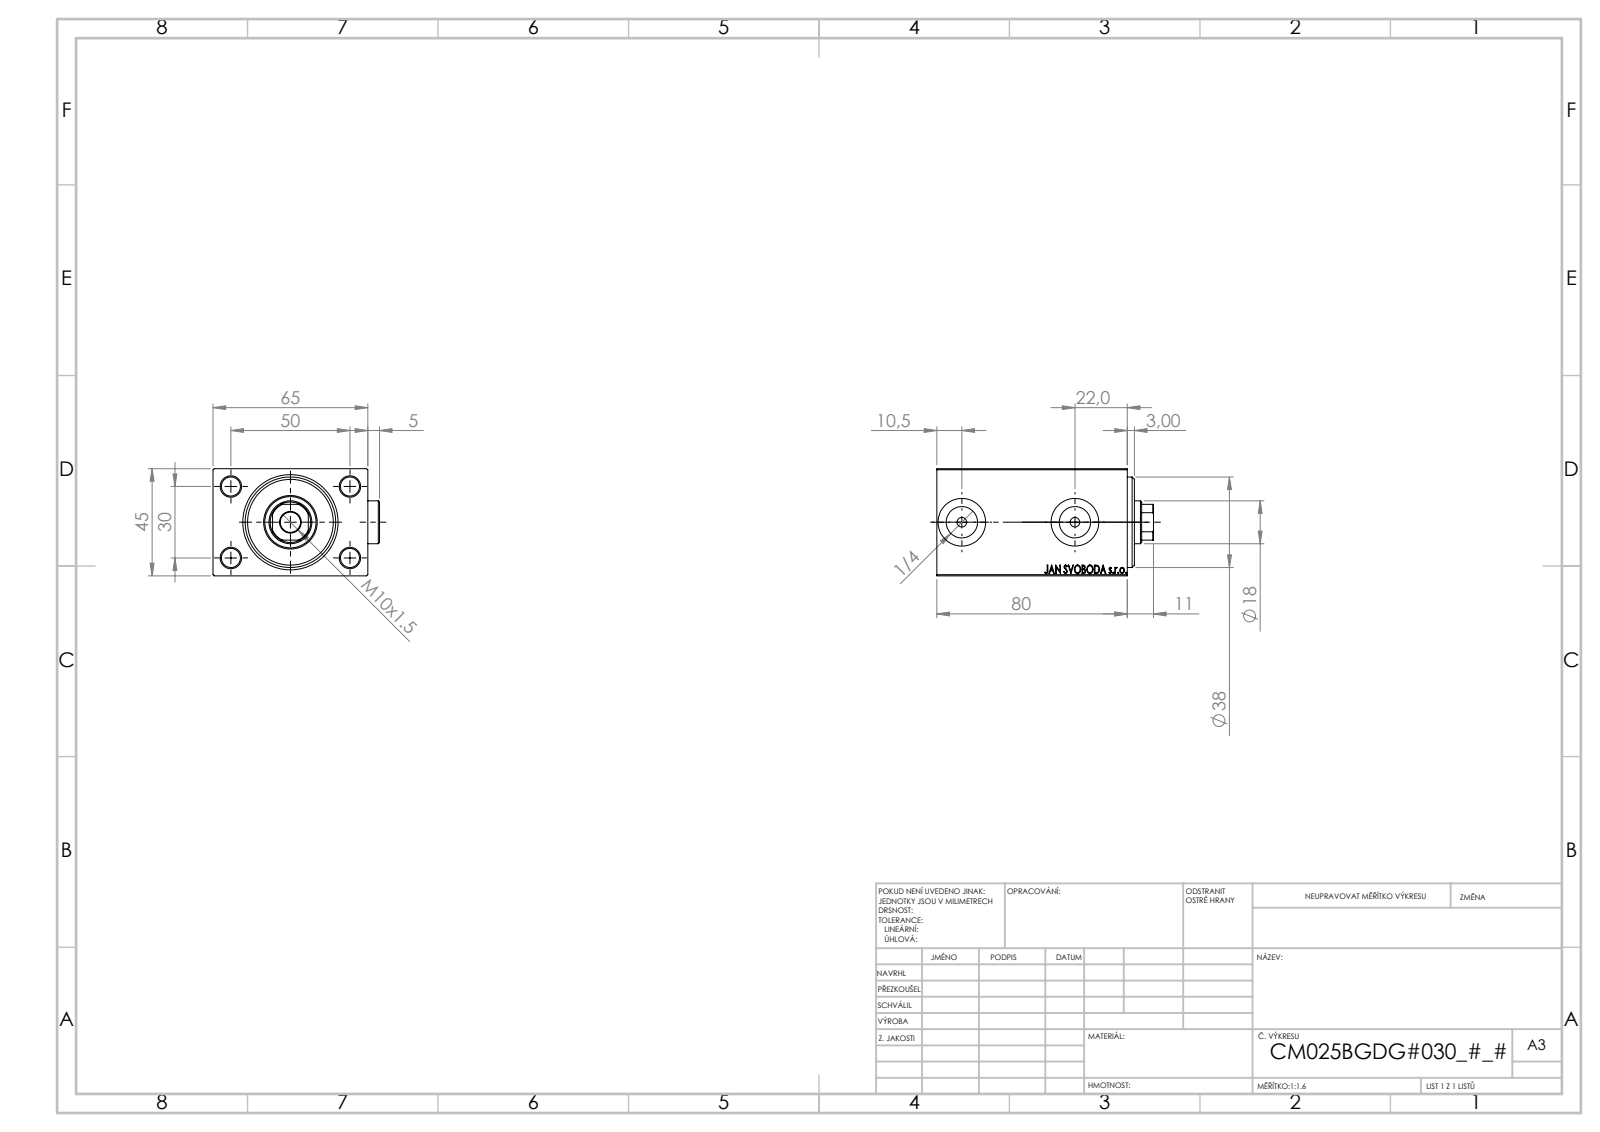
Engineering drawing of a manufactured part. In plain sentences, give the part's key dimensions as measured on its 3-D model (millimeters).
The part is named "V450CM_VC_B; V450CM_B_Body; V450CM_B_VCP; Zatka_OIL_PORT". Its 3-D file was written by "SolidWorks 2019 (CONFIG_CONTROL_DESIGN)". It is 5 solids with 935 faces: 435 planar, 70 cylindrical and 430 other. Overall it measures 91 by 69.9 by 45 millimeters. Its volume is 219 226 cubic millimeters and its surface area 47 448 square millimeters. Round holes: 4 of diameter 8, 2 of diameter 4, 2 of diameter 13.16, 2 of diameter 20, 1 of diameter 8.5, 1 of diameter 18, 1 of diameter 21.5, 1 of diameter 22.5, 1 of diameter 25, 1 of diameter 27, 1 of diameter 38. Round bosses or shafts: 2 of diameter 18. Partial cylindrical surfaces (rounded edges, fillets, slot ends): 1 of radius 8.5. The main face-to-face distances are 45, 65, 5, 6, 80, 69, 64.9, 75, 74, 8. The hole center spacings are 29.15, 30, 50, 58.31, 47.5.
